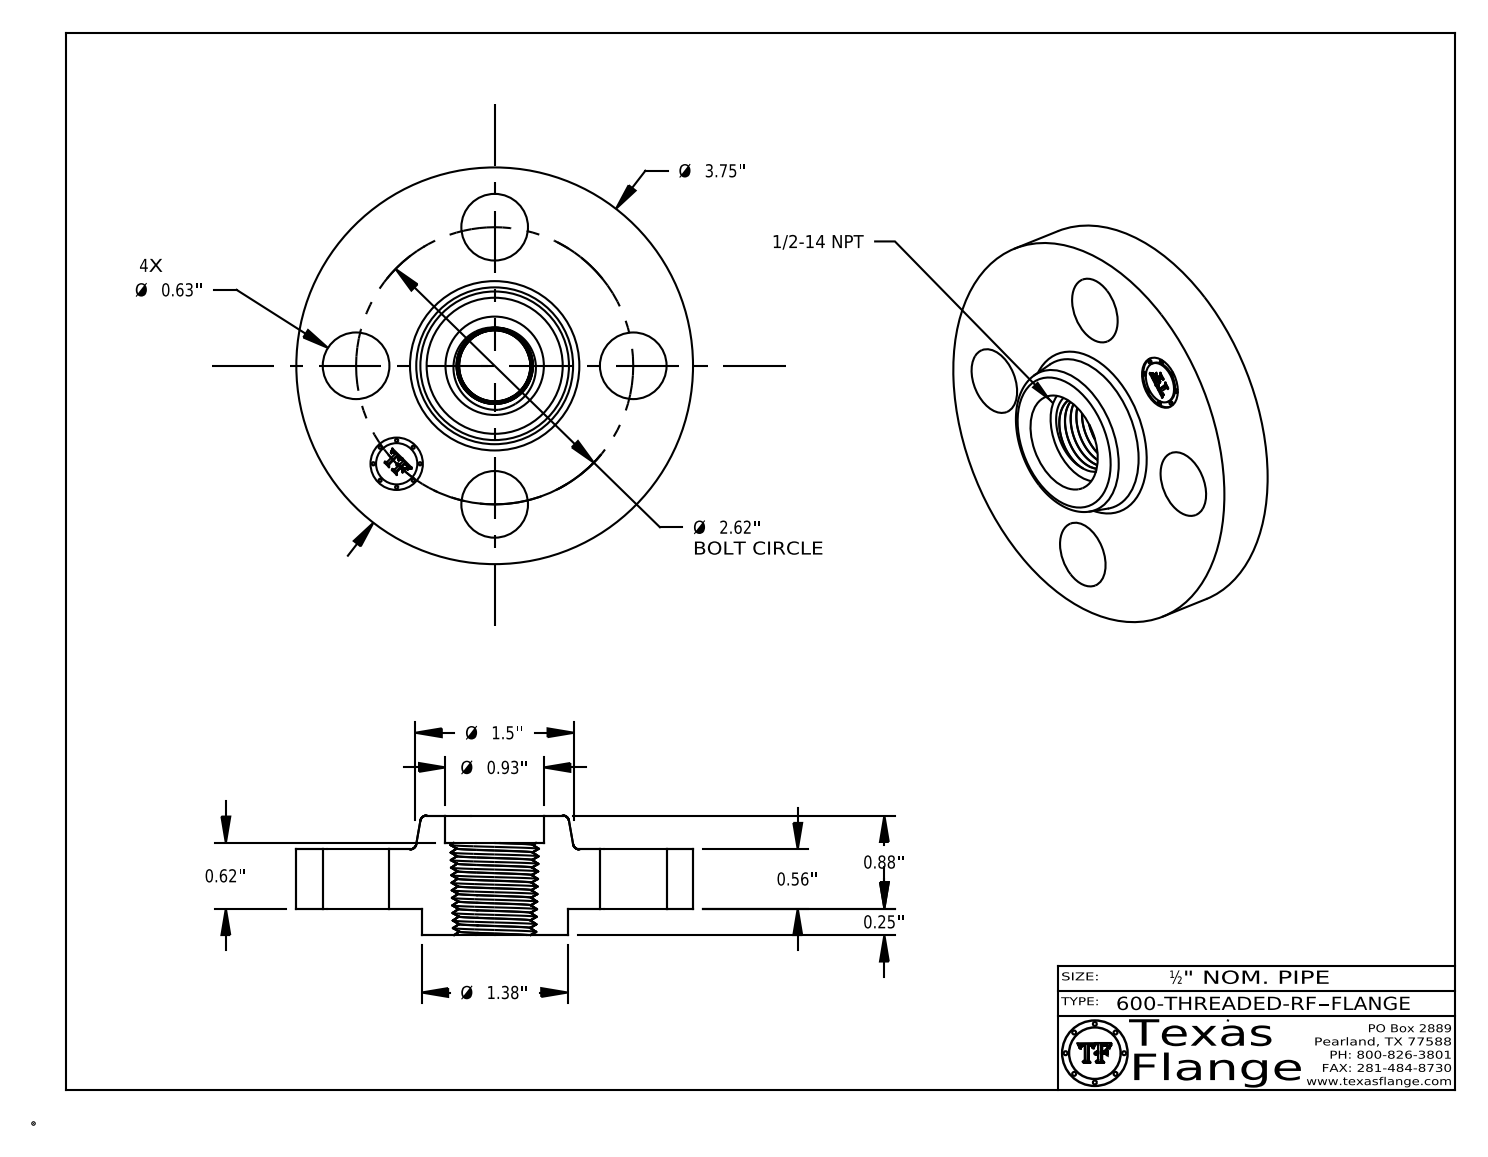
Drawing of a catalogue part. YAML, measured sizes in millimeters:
part_name: "600-THREADED-RF"
step_written_by: "CATIA V5 STEP AP214 (AUTOMOTIVE_DESIGN)"
units: millimeters
bodies: {solids: 1, faces: 538, planar: 370, cylindrical: 34, other: 134}
overall_size: [95.3, 95.3, 28.7]
volume: 95390
surface_area: 23600
round_holes:
  - {diameter: 16, count: 4}
  - {diameter: 12.6, count: 1}
  - {diameter: 23.6, count: 1}
round_bosses_or_shafts:
  - {diameter: 0.8, count: 8}
  - {diameter: 95.3, count: 1}
  - {diameter: 35.1, count: 1}
  - {diameter: 9.9, count: 1}
face_to_face_distances: [14.2, 6.4, 20.6, 28.7, 22.4, 8.1, 22.1, 15.7, 1.5, 6.6]
hole_center_spacings: [33.3, 47, 25.5, 61.5, 66.5, 33.3]
